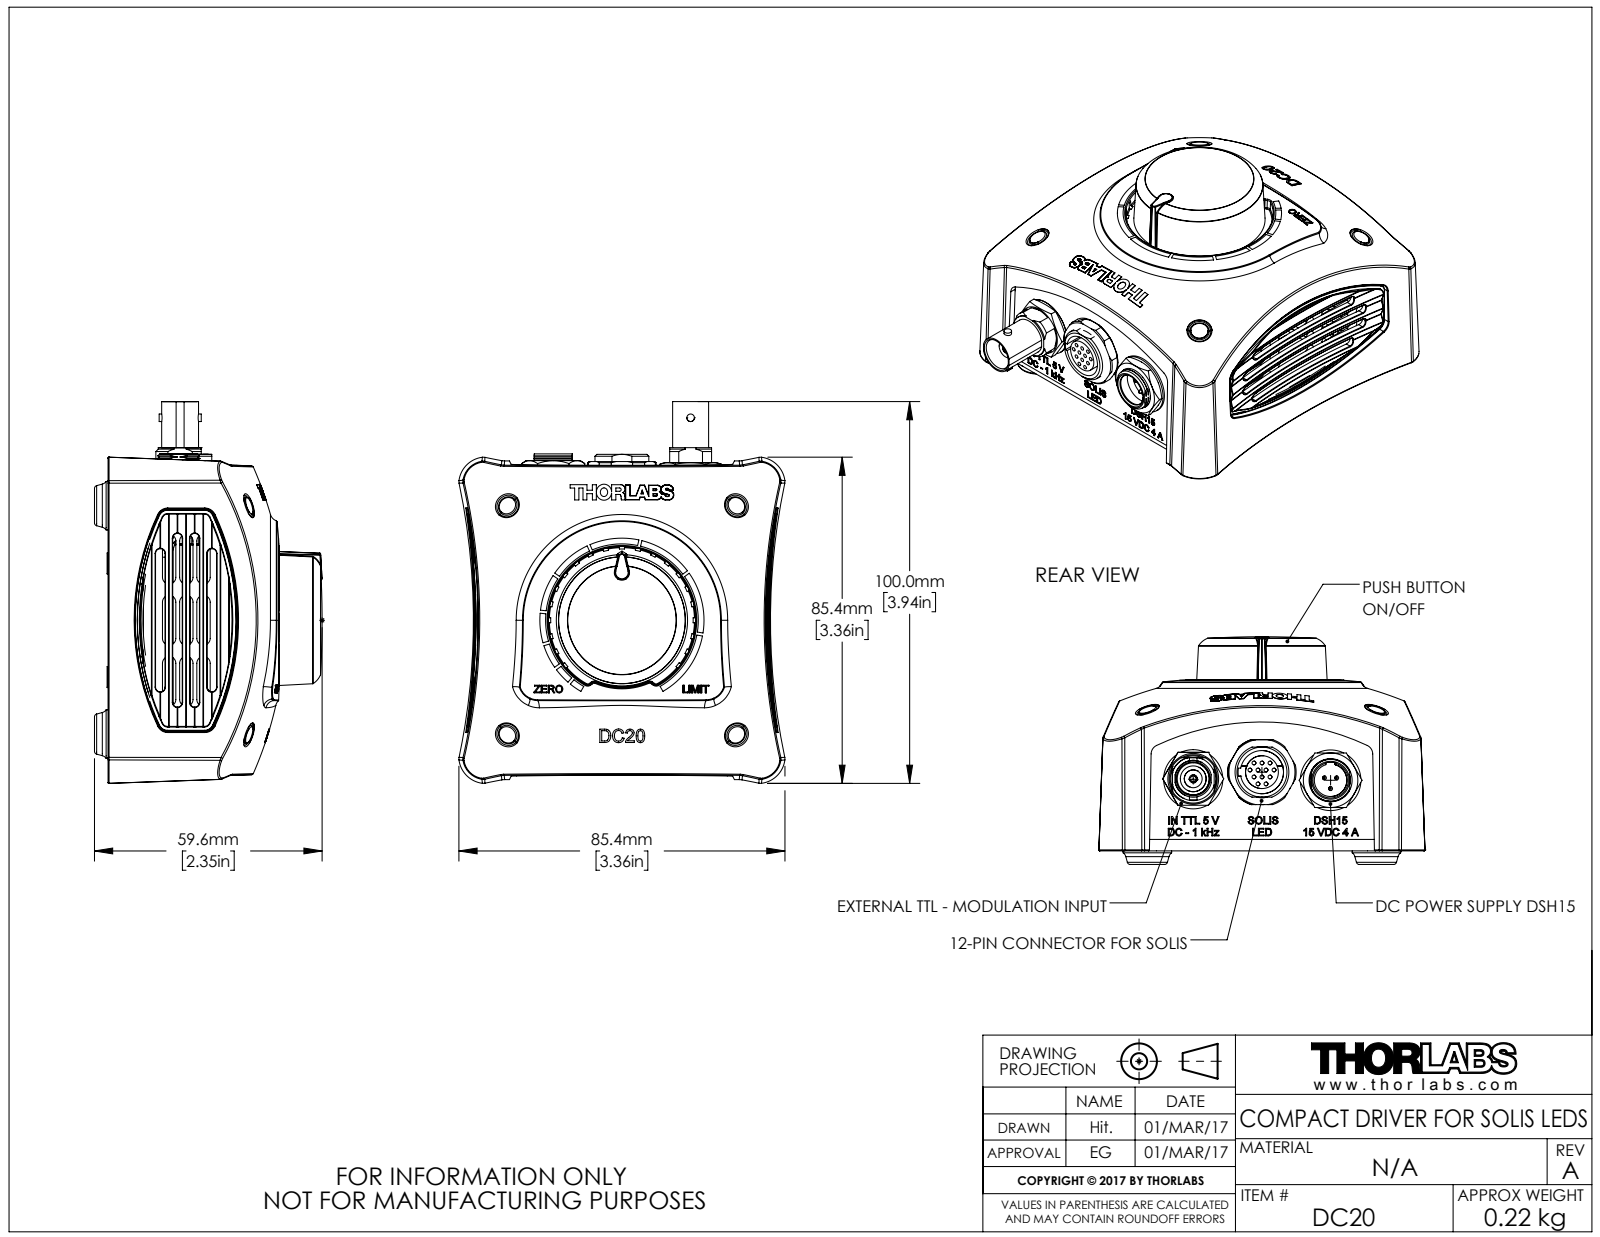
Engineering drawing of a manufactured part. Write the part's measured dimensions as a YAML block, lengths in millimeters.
part_name: "Zusammenbau DC20"
step_written_by: "SolidWorks 2016 (AUTOMOTIVE_DESIGN)"
units: millimeters
bodies: {solids: 32, faces: 4574, planar: 2204, cylindrical: 641, other: 1729}
overall_size: [99.96, 85.41, 59.62]
volume: 78238
surface_area: 86569
round_holes:
  - {diameter: 1, count: 12}
  - {diameter: 2.05, count: 12}
  - {diameter: 2.7, count: 4}
  - {diameter: 3, count: 4}
  - {diameter: 4.7, count: 4}
  - {diameter: 6, count: 4}
  - {diameter: 2.01, count: 2}
  - {diameter: 12, count: 2}
  - {diameter: 0.97, count: 1}
  - {diameter: 2.08, count: 1}
  - {diameter: 2.5, count: 1}
  - {diameter: 2.9, count: 1}
round_bosses_or_shafts:
  - {diameter: 0.9, count: 13}
  - {diameter: 1.5, count: 10}
  - {diameter: 12.7, count: 4}
  - {diameter: 5.5, count: 4}
  - {diameter: 3, count: 4}
  - {diameter: 0.71, count: 4}
  - {diameter: 1.02, count: 3}
  - {diameter: 0.64, count: 3}
partial_cylinders:
  - {radius: 1.75, count: 54}
  - {radius: 3, count: 32}
  - {radius: 1.25, count: 16}
  - {radius: 1, count: 12}
  - {radius: 0.15, count: 8}
  - {radius: 0.76, count: 8}
  - {radius: 1.02, count: 8}
  - {radius: 2.42, count: 8}
face_to_face_distances: [2, 75.6, 4, 69.5, 77.6, 73.6, 71.5, 67.5, 30.1, 28.1]
hole_center_spacings: [2.1, 3.64, 4.2, 60, 2.12, 5.56, 3.19, 3.65]
